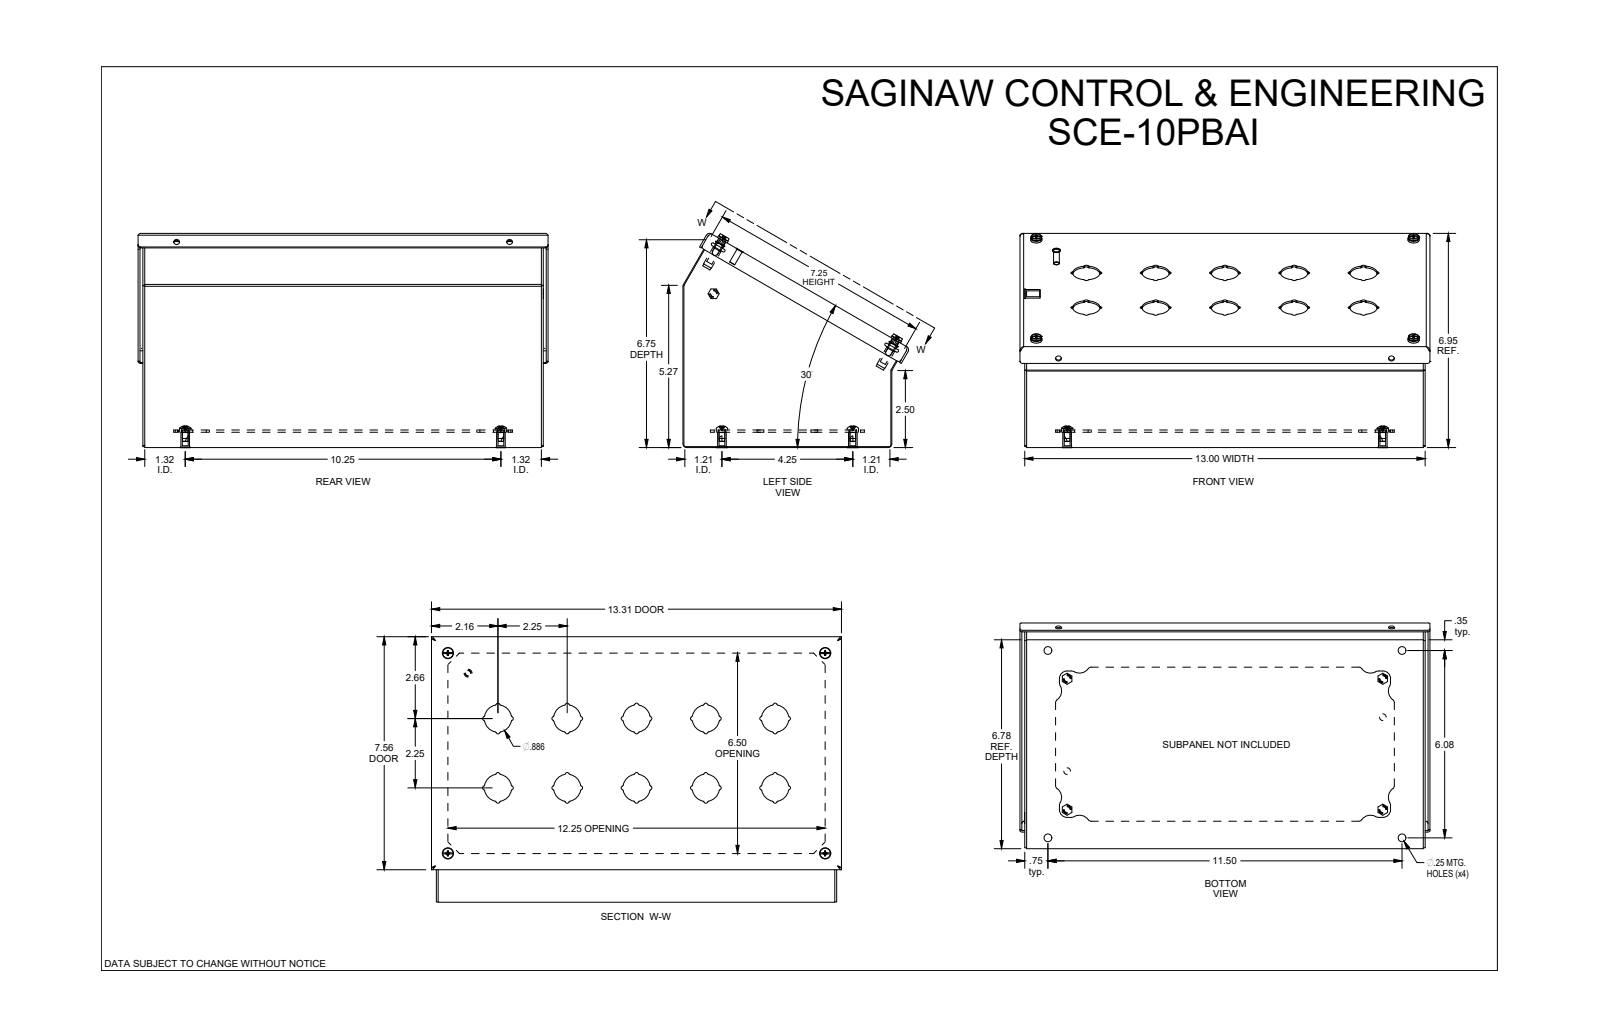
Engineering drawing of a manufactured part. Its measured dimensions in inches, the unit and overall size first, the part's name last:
Units: inches
Overall size (bounding box): 13.313 × 7.345 × 6.978
Round holes (diameter × count): ⌀0.25 ×12, ⌀0.19 ×9, ⌀0.22 ×4, ⌀0.266 ×4, ⌀0.281 ×4, ⌀0.317 ×4, ⌀0.187 ×2, ⌀0.218 ×2, ⌀0.193 ×1
Round bosses / shafts (diameter × count): ⌀0.28 ×5, ⌀0.362 ×4, ⌀0.34 ×4, ⌀0.292 ×4, ⌀0.27 ×4, ⌀0.26 ×4, ⌀0.256 ×1, ⌀0.188 ×1
Partial cylindrical surfaces — rounded edges, fillets, slot ends (radius × count): R0.04 ×84, R0.062 ×40, R0.06 ×20, R0.03 ×12, R0.25 ×12, R0.01 ×10, R0.443 ×10, R0.115 ×8
Main face-to-face distances: 0.06, 0.06, 12.94, 6.72, 0.496, 0.436, 0.075, 0.511, 0.571, 12.88
Hole centre spacings: 6.5, 12.25, 6.505, 10.914, 12.039, 12.25, 13.868, 1.108
Volume: 29.91 in³ · Surface area: 981.8 in²
Bodies: 20 solids, 727 faces (250 planar, 409 cylindrical, 68 other)
Part name (STEP PRODUCT): SCE-10PBAI
STEP written by: SolidWorks 2019 (AUTOMOTIVE_DESIGN)
